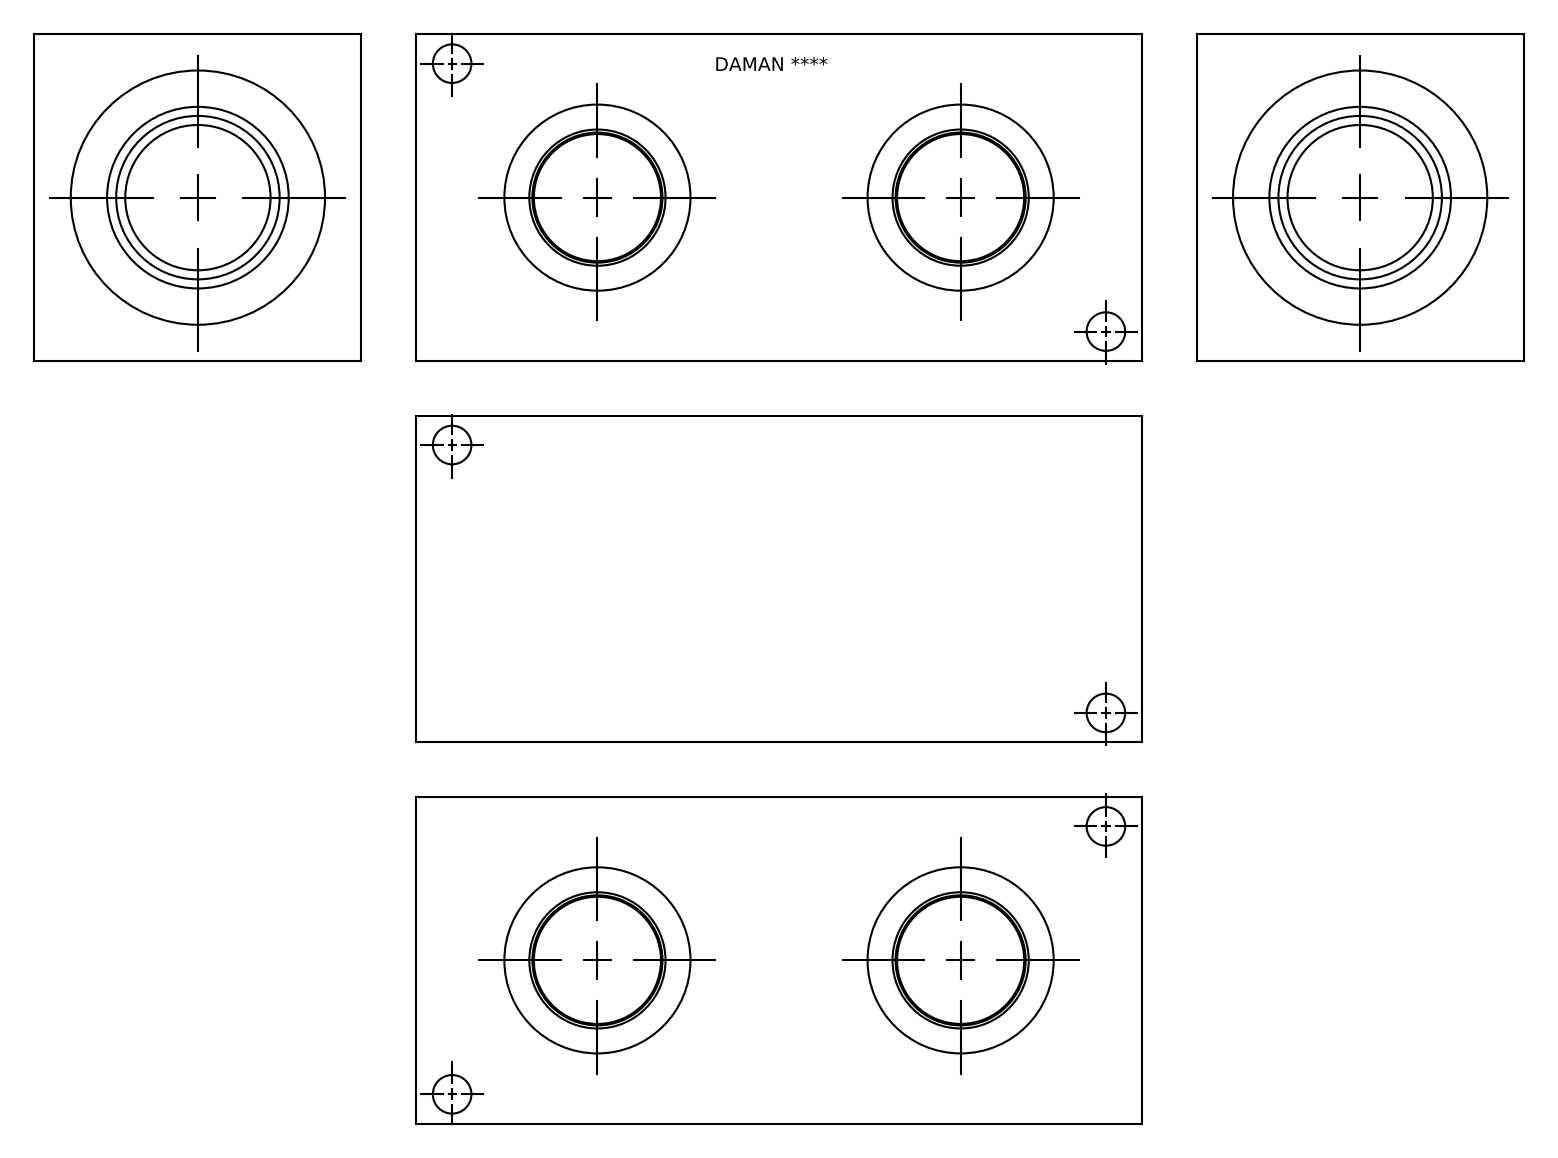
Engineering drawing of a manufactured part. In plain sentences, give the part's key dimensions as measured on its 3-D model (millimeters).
The part is named "Part_+H1800224S_3D". Its 3-D file was written by "Autodesk Inventor 2020 (AUTOMOTIVE_DESIGN)". It is 1 solid with 392 faces: 240 planar, 38 cylindrical and 114 other. Overall it measures 254 by 114.3 by 114.3 millimeters. Its volume is 2 738 000 cubic millimeters and its surface area 194 835 square millimeters. Round holes: 4 of diameter 13.49, 2 of diameter 42.88, 2 of diameter 45.57, 2 of diameter 47.62, 2 of diameter 48.06, 2 of diameter 65.13, 1 of diameter 50.8, 1 of diameter 61.44, 1 of diameter 63.5, 1 of diameter 63.96, 1 of diameter 88.14. The main face-to-face distances are 114.3, 0.79, 254, 113.51, 253.21, 112.72, 252.42, 19.84, 19.05, 94.46. The hole center spacings are 69.1, 183.87, 247.05, 127.
